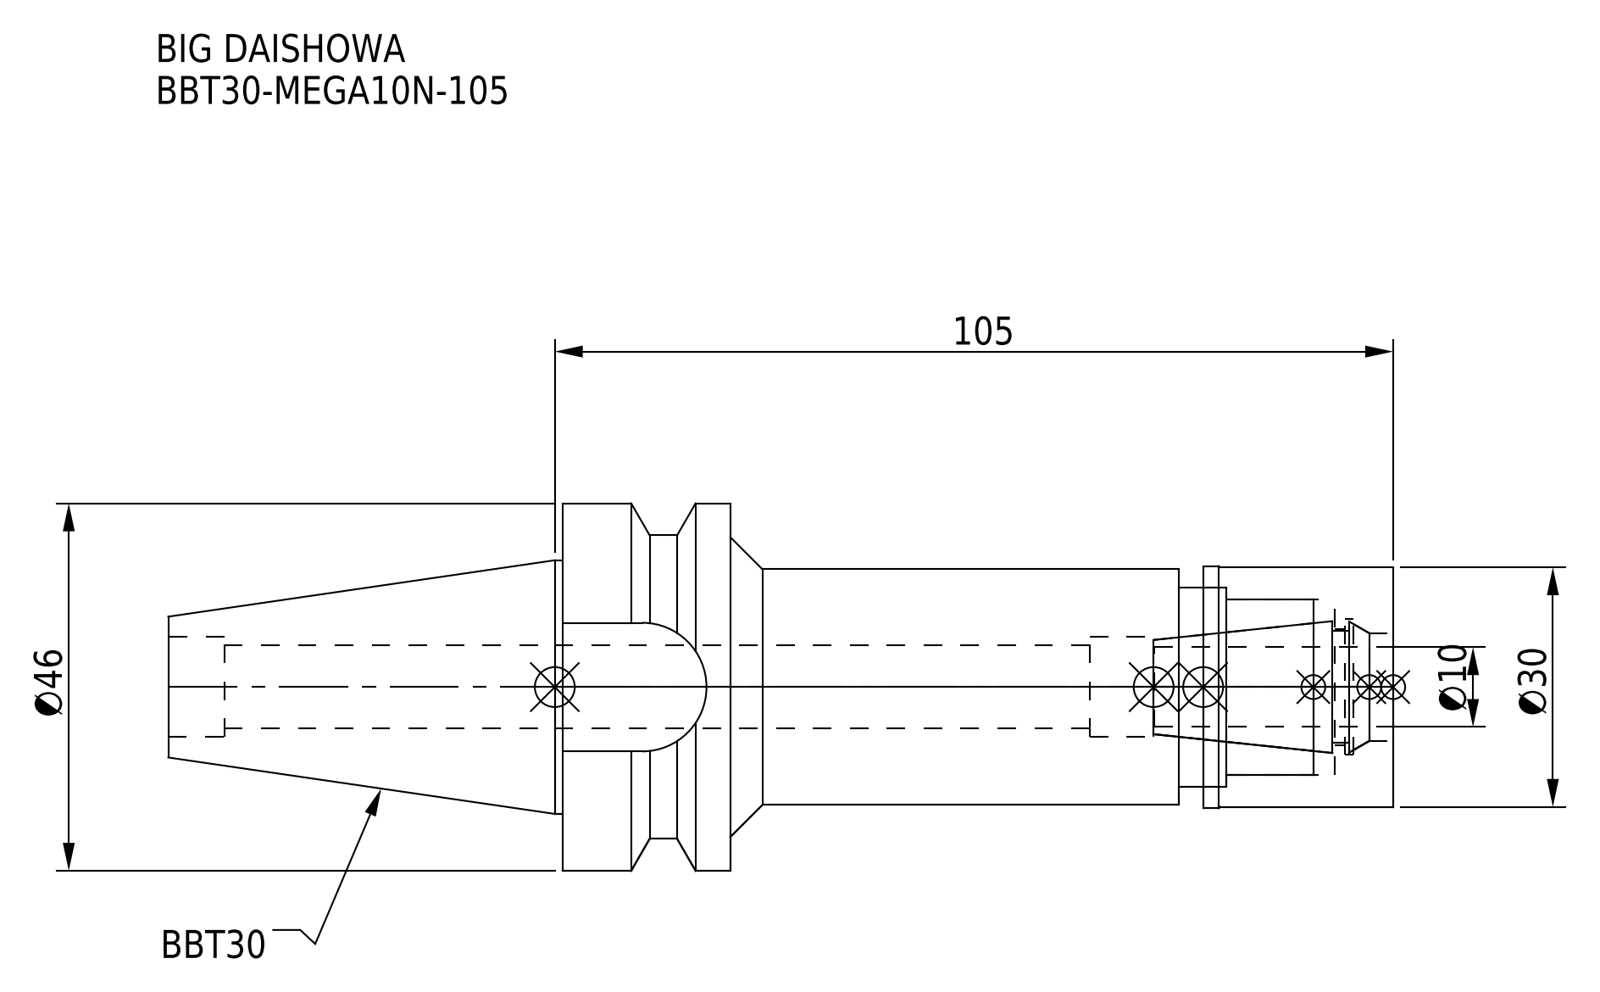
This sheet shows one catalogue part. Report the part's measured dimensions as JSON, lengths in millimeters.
{"part_name": "BBT30-MEGA10N-105; BBT30-MEGA10N-105_1.stp; DXF_TEMP_ASSY_ASM_4_ASM.stp; BBT30-MEGA10N-105-100-FreeParts (+3 more)", "step_written_by": "SolidWorks 2019 (CONFIG_CONTROL_DESIGN)", "units": "millimeters", "bodies": {"solids": 2, "faces": 73, "planar": 21, "cylindrical": 38, "other": 14}, "overall_size": [153.4, 46, 46], "volume_mm3": 95034, "surface_area_mm2": 26210, "round_holes": [[10.4, 1], [12.5, 1], [13.5, 1], [14.5, 1], [17, 1], [22, 1], [25, 1]], "round_bosses_or_shafts": [[46, 1], [31.75, 1], [30.3, 1], [30, 1], [29.5, 1]], "partial_cylinders_radius": [[8.05, 1], [19, 1]], "face_to_face_distances": [104, 83, 21, 32.6, 23.8, 59.2, 80.2, 20.9, 2.9, 62.1]}
